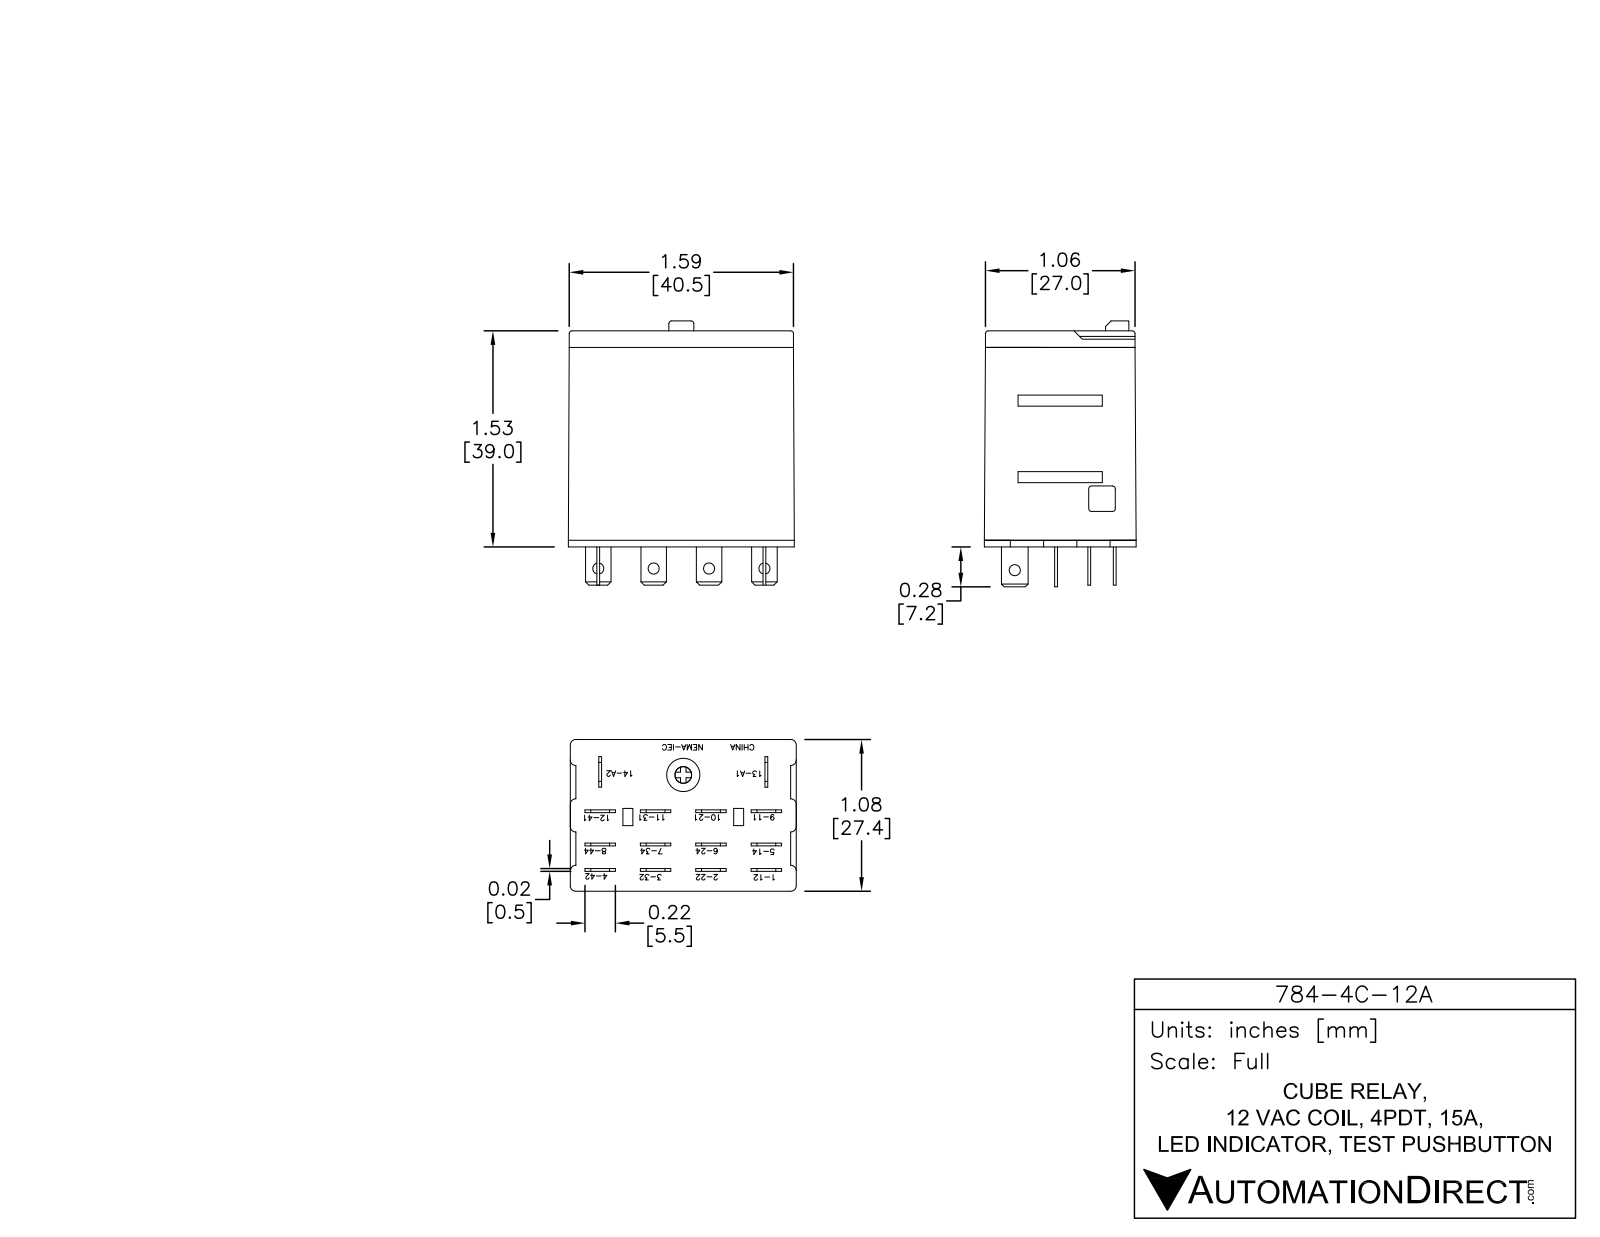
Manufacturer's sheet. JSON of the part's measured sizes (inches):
{"part_name": "784-4C-12A", "step_written_by": "SolidWorks 2013 (AUTOMOTIVE_DESIGN)", "units": "inches", "bodies": {"solids": 18, "faces": 399, "planar": 303, "cylindrical": 56, "other": 40}, "overall_size": [1.854, 1.604, 1.087], "volume_in3": 2.684, "surface_area_in2": 21.03, "round_holes": [[0.073, 5], [0.049, 1], [0.207, 1]], "round_bosses_or_shafts": [[0.196, 1], [0.033, 1]], "partial_cylinders_radius": [[0.02, 10], [0.42, 1]], "face_to_face_distances": [1.368, 1.083, 0.069, 1.437, 1.604, 0.118, 1.486, 1.555, 0.02, 0.413], "hole_center_spacings": [0.394, 0.396, 0.397, 0.751, 0.791, 0.793, 1.187]}
